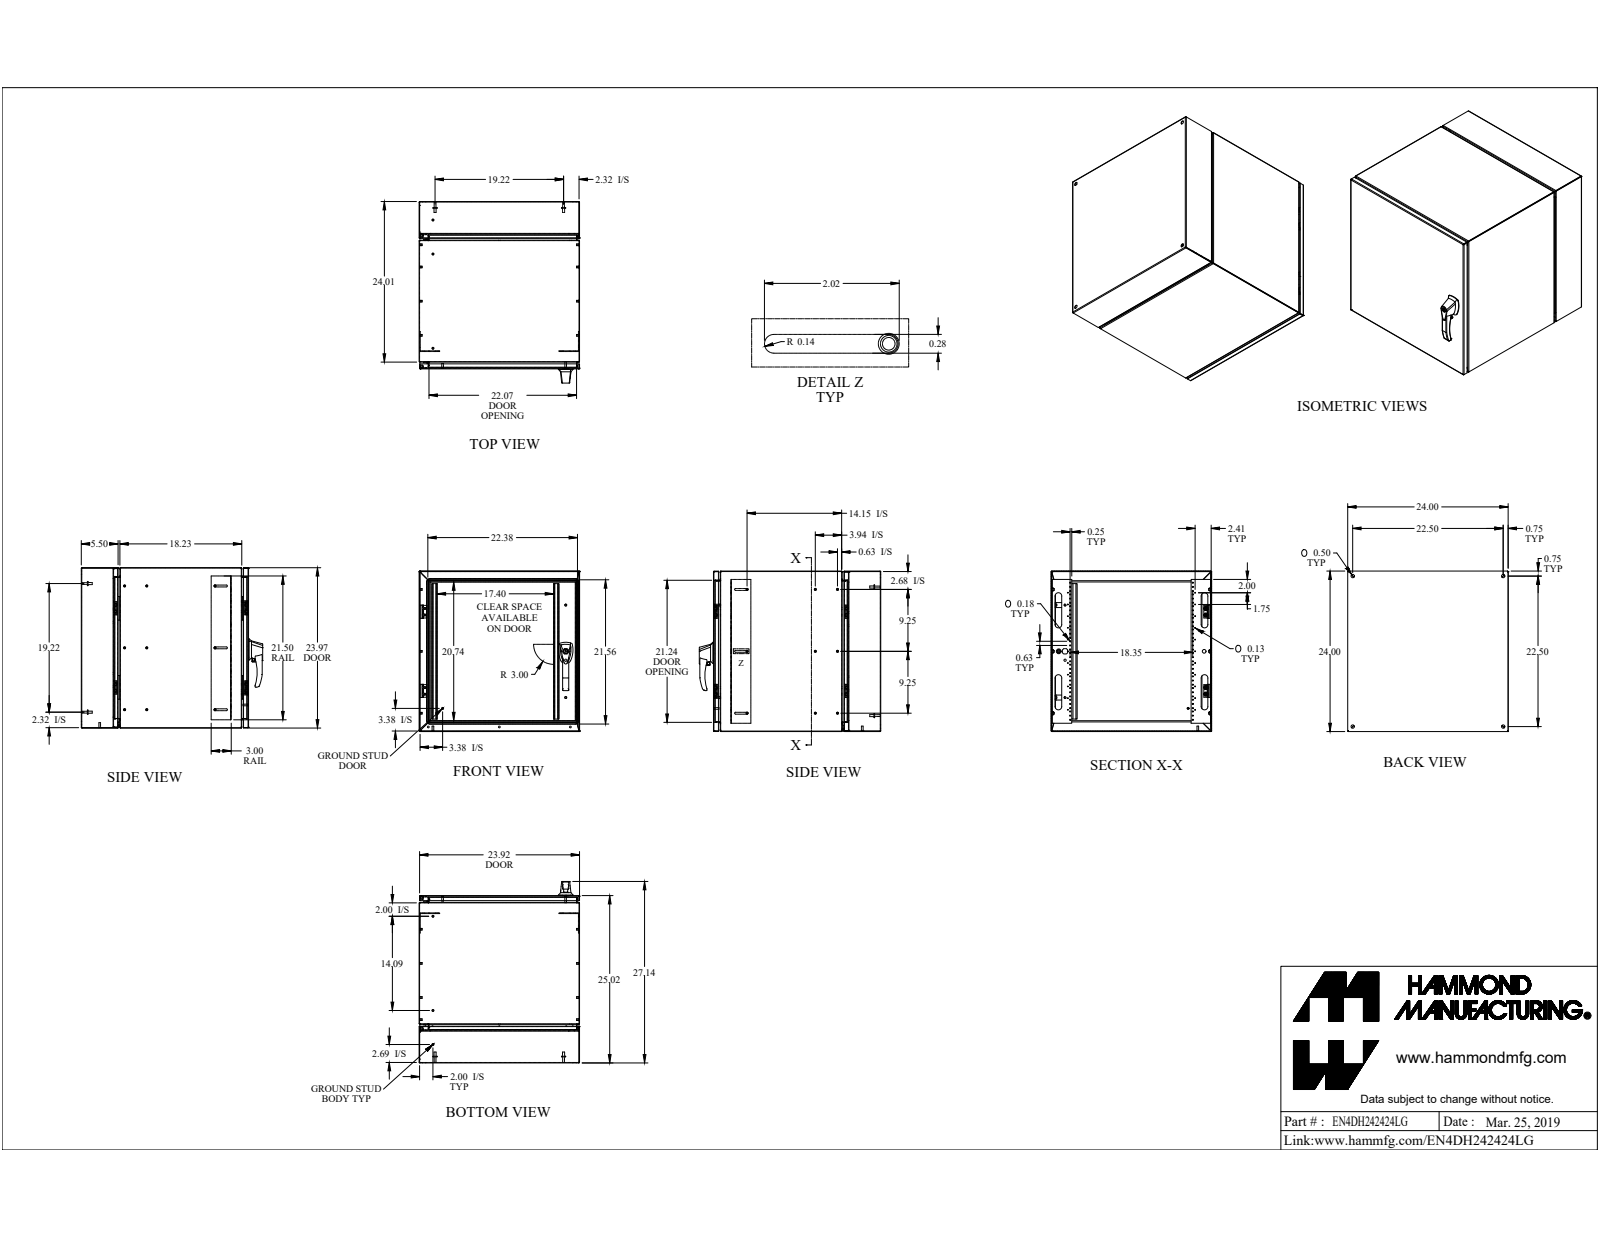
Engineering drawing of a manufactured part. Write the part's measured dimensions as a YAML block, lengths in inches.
part_name: "EN4DH242424LG"
step_written_by: "SolidWorks 2019 (CONFIG_CONTROL_DESIGN)"
units: inches
bodies: {solids: 180, faces: 3652, planar: 2004, cylindrical: 937, other: 711}
overall_size: [27.135, 24.001, 24]
volume: 375
surface_area: 9833
round_holes:
  - {diameter: 0.177, count: 72}
  - {diameter: 0.125, count: 22}
  - {diameter: 0.25, count: 17}
  - {diameter: 0.196, count: 15}
  - {diameter: 0.188, count: 8}
  - {diameter: 0.194, count: 8}
  - {diameter: 0.237, count: 8}
  - {diameter: 0.257, count: 7}
  - {diameter: 0.275, count: 7}
  - {diameter: 0.265, count: 5}
  - {diameter: 0.276, count: 4}
  - {diameter: 0.281, count: 4}
round_bosses_or_shafts:
  - {diameter: 0.25, count: 24}
  - {diameter: 0.313, count: 16}
  - {diameter: 0.236, count: 10}
  - {diameter: 0.625, count: 8}
  - {diameter: 0.472, count: 8}
  - {diameter: 0.433, count: 8}
  - {diameter: 0.187, count: 8}
  - {diameter: 0.281, count: 6}
partial_cylinders:
  - {radius: 0.036, count: 37}
  - {radius: 0.108, count: 37}
  - {radius: 0.141, count: 18}
  - {radius: 0.25, count: 18}
  - {radius: 0.125, count: 17}
  - {radius: 0.06, count: 16}
  - {radius: 0.043, count: 12}
  - {radius: 0.079, count: 12}
face_to_face_distances: [0.072, 23.928, 23.856, 24.948, 24, 24.876, 25.02, 20.188, 4.76, 0.095]
hole_center_spacings: [2.25, 3.5, 9.25, 16.384, 22.5, 1.934, 11.815, 13.523]
